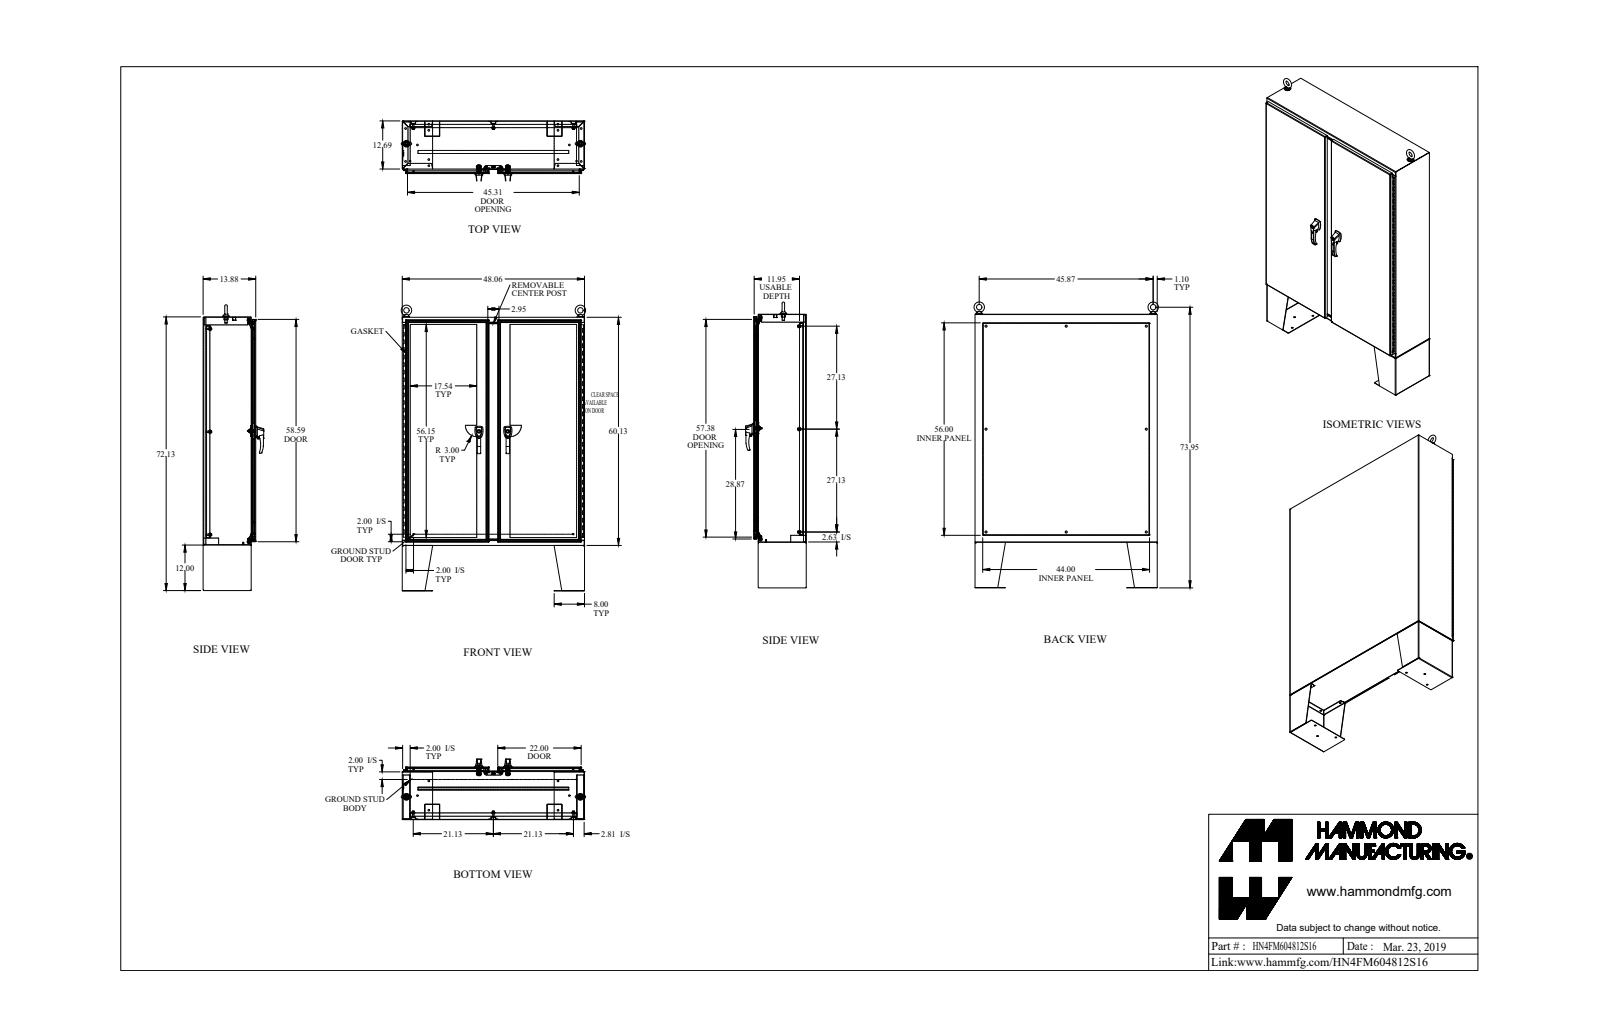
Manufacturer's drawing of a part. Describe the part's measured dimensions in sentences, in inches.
The part is named "HN4FM604812S16". Its 3-D file was written by "SolidWorks 2018 (AUTOMOTIVE_DESIGN)". It is 134 solids with 3784 faces: 1748 planar, 1675 cylindrical and 361 other. Overall it measures 75.321 by 48.606 by 15.99 inches. Its volume is 1 476 cubic inches and its surface area 29 833 square inches. Round holes: 20 of diameter 0.304, 14 of diameter 0.437, 8 of diameter 0.307, 8 of diameter 0.35, 8 of diameter 0.563, 7 of diameter 0.445, 6 of diameter 0.25, 4 of diameter 0.281, 4 of diameter 0.313, 4 of diameter 0.39, 3 of diameter 0.201, 3 of diameter 0.313. Round bosses or shafts: 10 of diameter 1, 8 of diameter 0.65, 8 of diameter 0.375, 8 of diameter 0.332, 4 of diameter 0.75, 4 of diameter 0.625, 4 of diameter 0.44, 4 of diameter 0.37. Partial cylindrical surfaces (rounded edges, fillets, slot ends): 33 of radius 0.5, 32 of radius 0.018, 32 of radius 0.125, 28 of radius 0.06, 27 of radius 0.048, 27 of radius 0.143, 12 of radius 0.03, 12 of radius 0.09. The main face-to-face distances are 0.095, 13.78, 13.685, 13.875, 0.125, 11.998, 1.782, 1.687, 12.093, 1.657. The hole center spacings are 6, 12, 18, 24, 30, 46.571, 1.61, 4.888.
